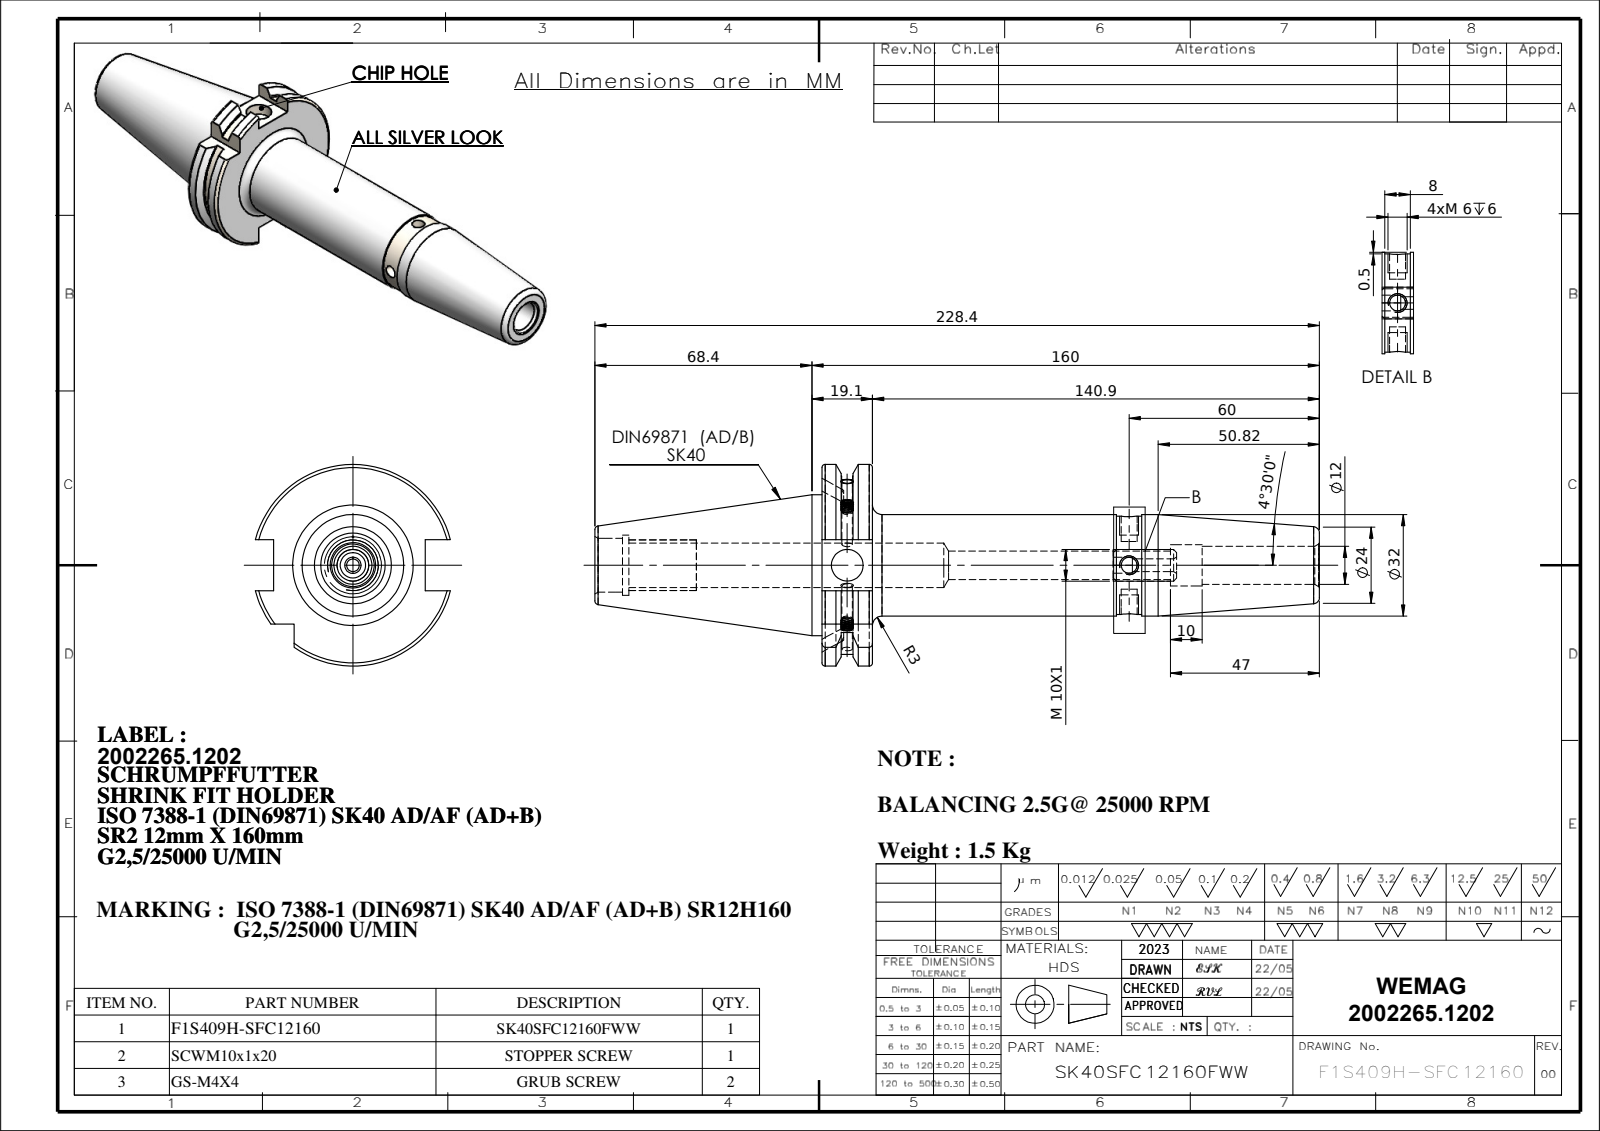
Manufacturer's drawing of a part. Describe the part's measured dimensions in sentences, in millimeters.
The part is named "SCWM10X1; SK40SFC12160FWW; GS-M4X4_DIN 913 - M4 x 4-N; 91406-SR212160". Its 3-D file was written by "SolidWorks 2018 (CONFIG_CONTROL_DESIGN)". It is 4 solids with 233 faces: 63 planar, 70 cylindrical and 100 other. Overall it measures 228.4 by 63.55 by 61.48 millimeters. Its volume is 189 089 cubic millimeters and its surface area 41 008 square millimeters. Round holes: 2 of diameter 5, 1 of diameter 3.3, 1 of diameter 4, 1 of diameter 9, 1 of diameter 10, 1 of diameter 11.99, 1 of diameter 12.99, 1 of diameter 14, 1 of diameter 17, 1 of diameter 19. Round bosses or shafts: 2 of diameter 4, 1 of diameter 44.45, 1 of diameter 32, 1 of diameter 31, 1 of diameter 10. Partial cylindrical surfaces (rounded edges, fillets, slot ends): 1 of radius 28.12, 1 of radius 31.77. The main face-to-face distances are 15.9, 16.1, 47.8, 156.8, 140.9, 71.6, 87.5, 228.4, 10.7, 60.9. The hole center spacings are 88.85.
